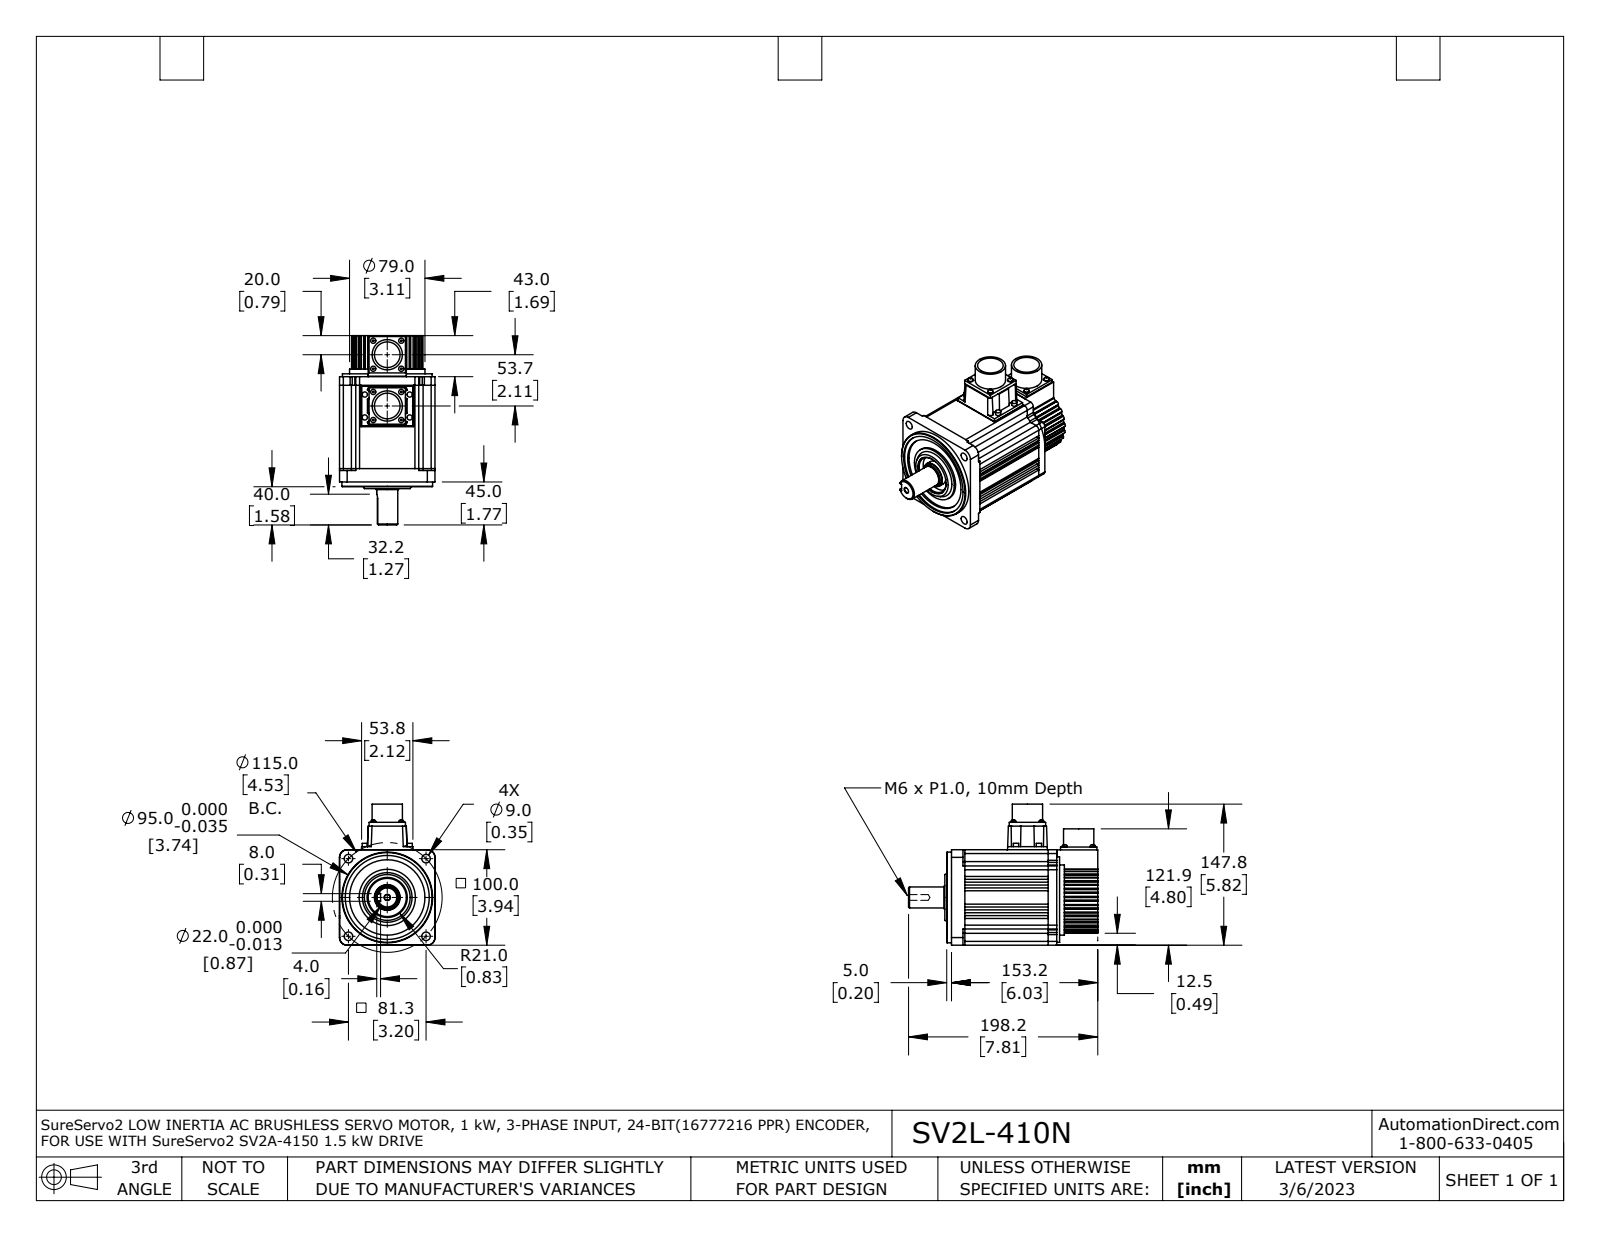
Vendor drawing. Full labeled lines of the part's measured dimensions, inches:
Part name (STEP PRODUCT): SV2L-x10N coord fxt
STEP written by: SolidWorks 2021 (AUTOMOTIVE_DESIGN)
Units: inches
Bodies: 2 solids, 566 faces (274 planar, 240 cylindrical, 52 other)
Overall size (bounding box): 7.805 × 5.817 × 3.937
Volume: 78.35 in³ · Surface area: 171.3 in²
Round holes (diameter × count): ⌀0.354 ×4, ⌀1.058 ×2, ⌀0.236 ×1, ⌀0.984 ×1, ⌀1.024 ×1, ⌀1.575 ×1, ⌀1.654 ×1, ⌀3.11 ×1, ⌀3.465 ×1
Round bosses / shafts (diameter × count): ⌀0.217 ×6, ⌀0.213 ×6, ⌀1.25 ×2, ⌀3.74 ×1, ⌀3.701 ×1, ⌀3.11 ×1, ⌀2.323 ×1, ⌀1.063 ×1
Partial cylindrical surfaces — rounded edges, fillets, slot ends (radius × count): R0.039 ×44, R0.079 ×21, R0.157 ×13, R0.118 ×8, R1.397 ×1, R1.949 ×1, R1.968 ×1, R1.969 ×1
Main face-to-face distances: 0.669, 0.118, 3.937, 3.268, 0.236, 2.598, 1.575, 0.433, 1.378, 6.033
Hole centre spacings: 2.264, 3.202, 4.528, 2.113
